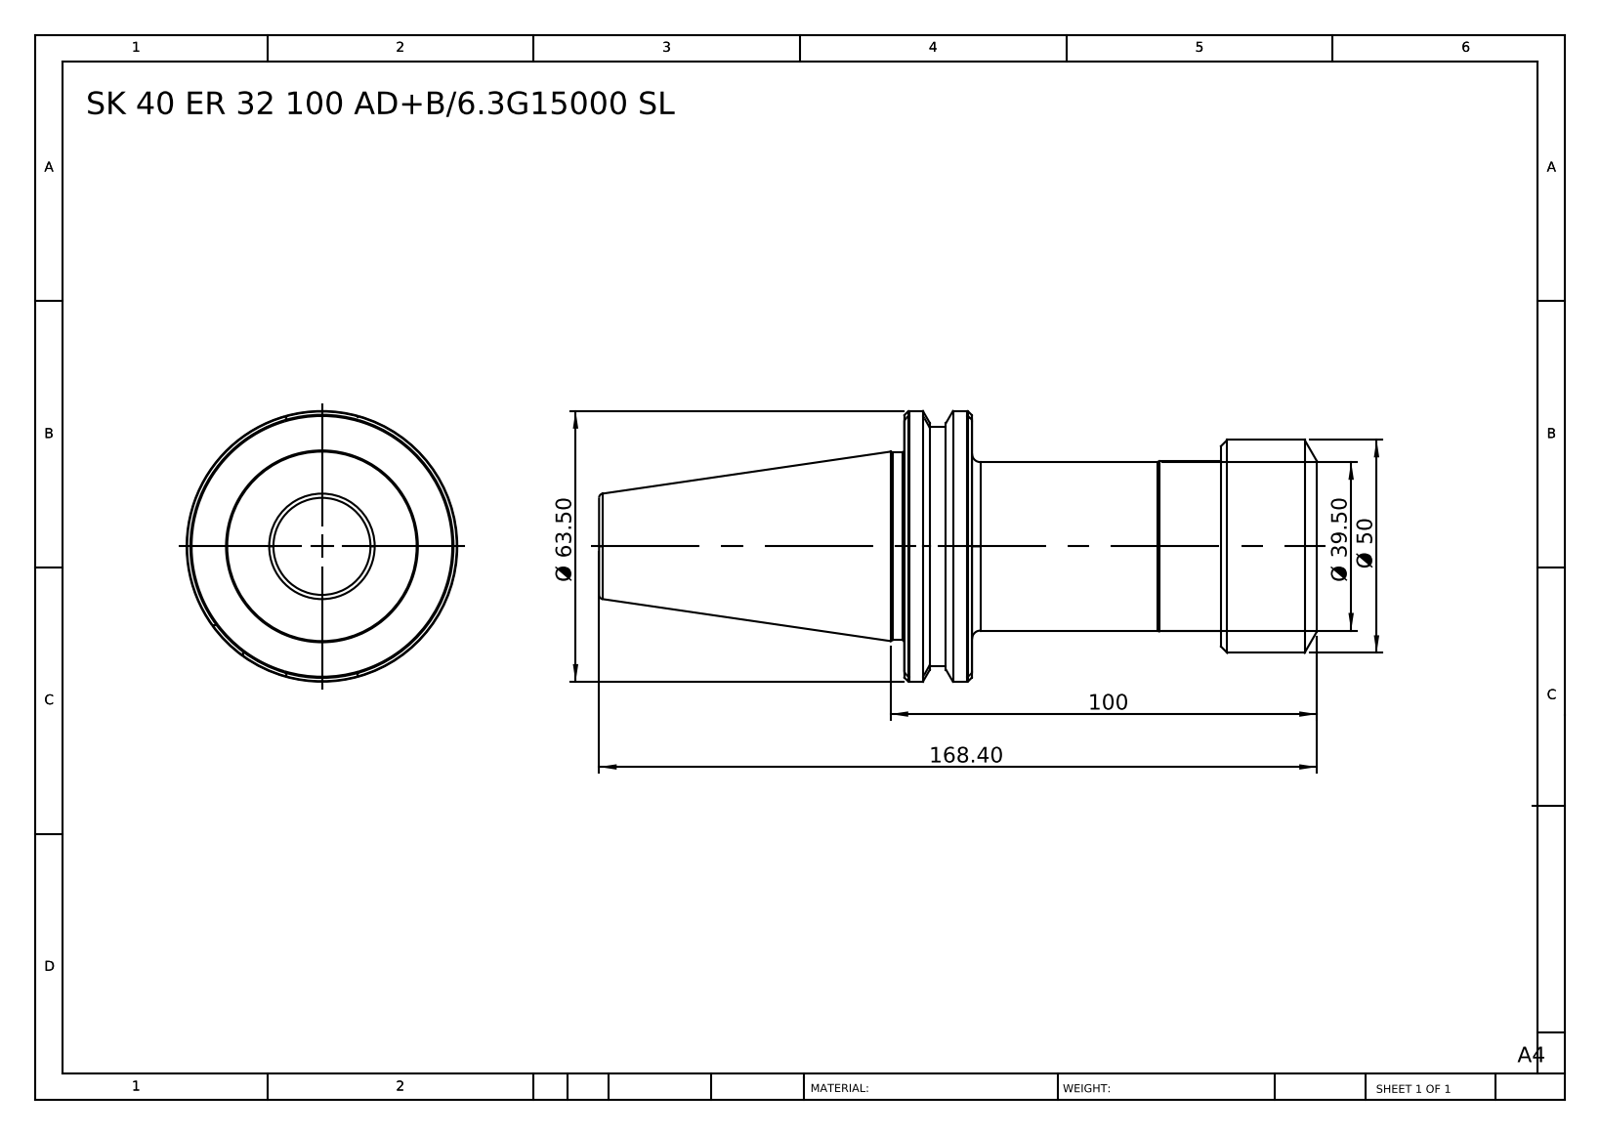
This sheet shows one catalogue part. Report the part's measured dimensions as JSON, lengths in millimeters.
{"part_name": "SK 40 ER 32 100 AD-6.3G15000 SL", "step_written_by": "SolidWorks 2014 (CONFIG_CONTROL_DESIGN)", "units": "millimeters", "bodies": {"solids": 1, "faces": 89, "planar": 7, "cylindrical": 14, "other": 68}, "overall_size": [168.4, 63.5, 63.5], "volume_mm3": 232083, "surface_area_mm2": 28592, "round_bosses_or_shafts": [[63.5, 1], [56, 1], [50, 1], [44, 1], [39.9, 1], [39.5, 1]], "face_to_face_distances": [15.9, 80.9, 96.8, 22.5, 58.4, 74.3, 168.4, 145.9, 87.5, 71.6]}
